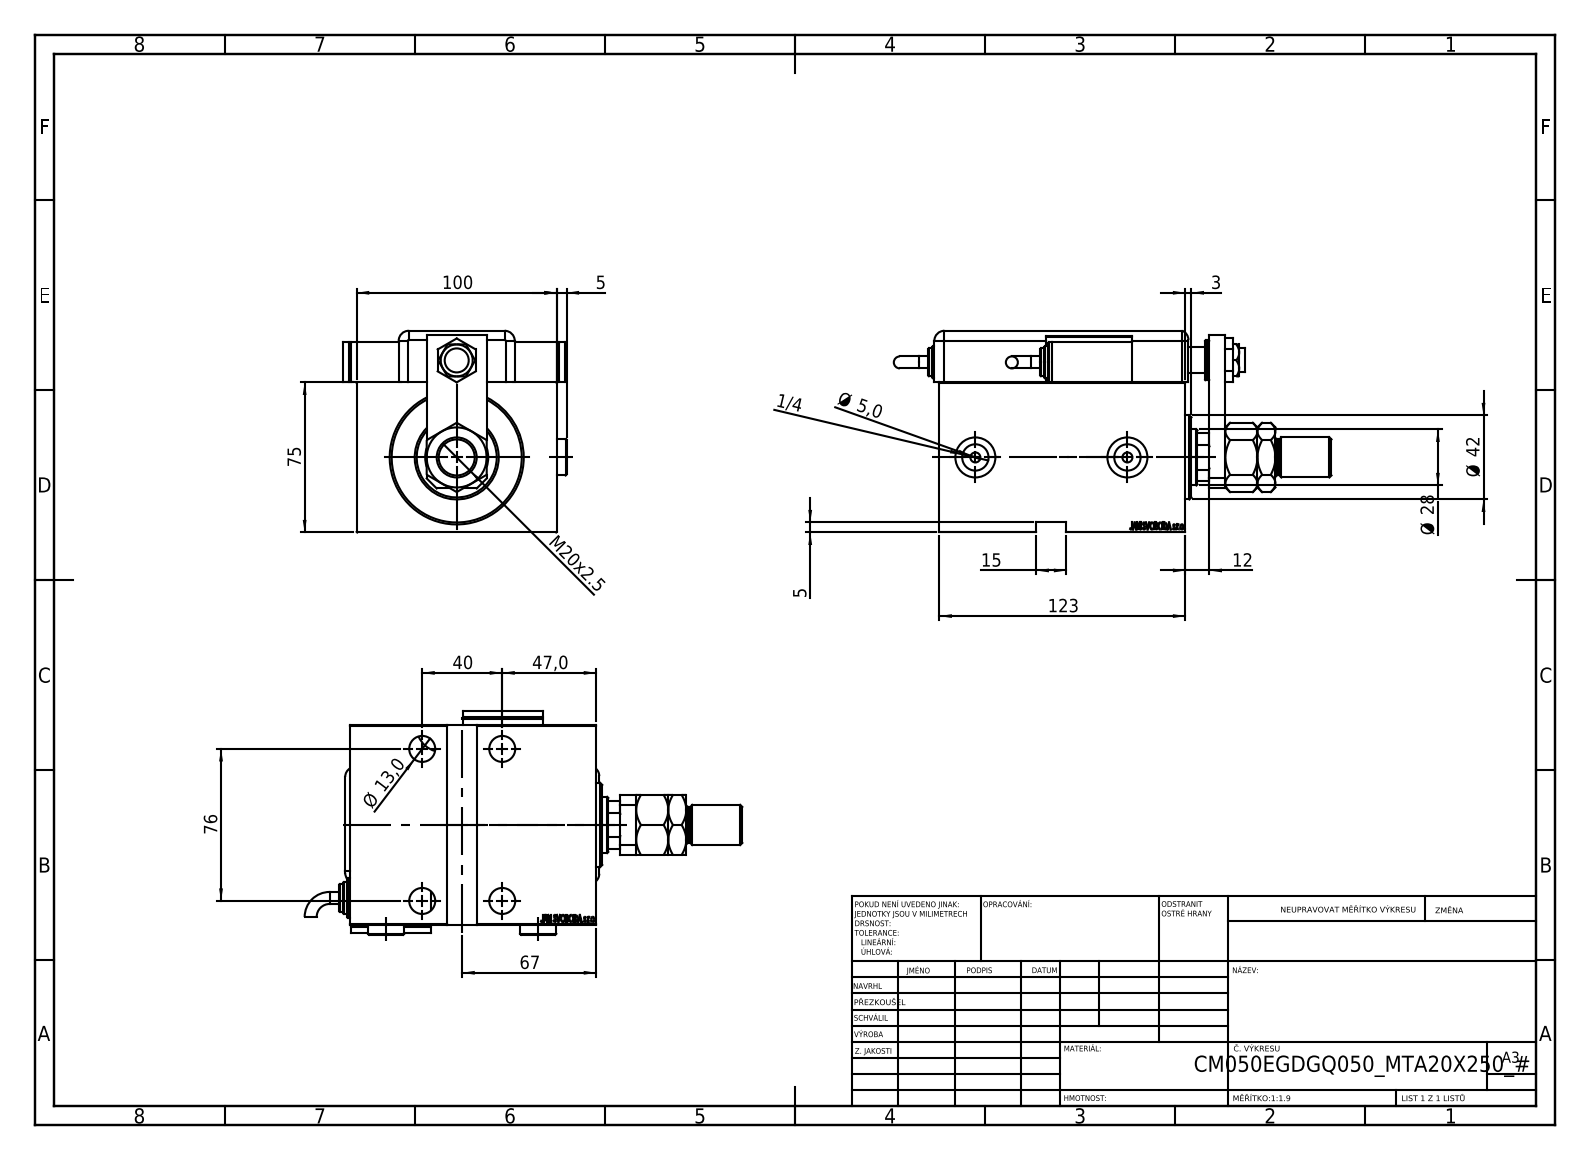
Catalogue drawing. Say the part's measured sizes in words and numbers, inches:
The part is named "SWITCH DIM A_G; SWITCH_Q_FRONT_BACK; V450CM_VC_B; Q_T_W_MTA (+7 more)". Its 3-D file was written by "SolidWorks 2019 (CONFIG_CONTROL_DESIGN)". It is 16 solids with 1345 faces: 667 planar, 127 cylindrical and 551 other. Overall it measures 8.613 by 4.406 by 3.969 inches. Its volume is 59.77 cubic inches and its surface area 293.5 square inches. Round holes: 5 of diameter 0.512, 4 of diameter 0.748, 3 of diameter 0.787, 2 of diameter 0.157, 2 of diameter 0.197, 2 of diameter 0.315, 2 of diameter 0.518, 1 of diameter 0.472, 1 of diameter 0.551, 1 of diameter 0.728, 1 of diameter 1.102, 1 of diameter 1.24. Round bosses or shafts: 3 of diameter 0.787, 3 of diameter 0.709, 2 of diameter 0.63, 2 of diameter 0.551, 2 of diameter 0.236, 1 of diameter 2.047, 1 of diameter 1.654. Partial cylindrical surfaces (rounded edges, fillets, slot ends): 9 of radius 0.197, 1 of radius 0.394, 1 of radius 0.531. The main face-to-face distances are 0.118, 2.953, 3.937, 0.551, 4.843, 3.969, 1.016, 0.787, 4.291, 0.984. The hole center spacings are 2.992, 1.575, 1.858, 2.41, 3.263, 3.381, 3.606, 0.787.
